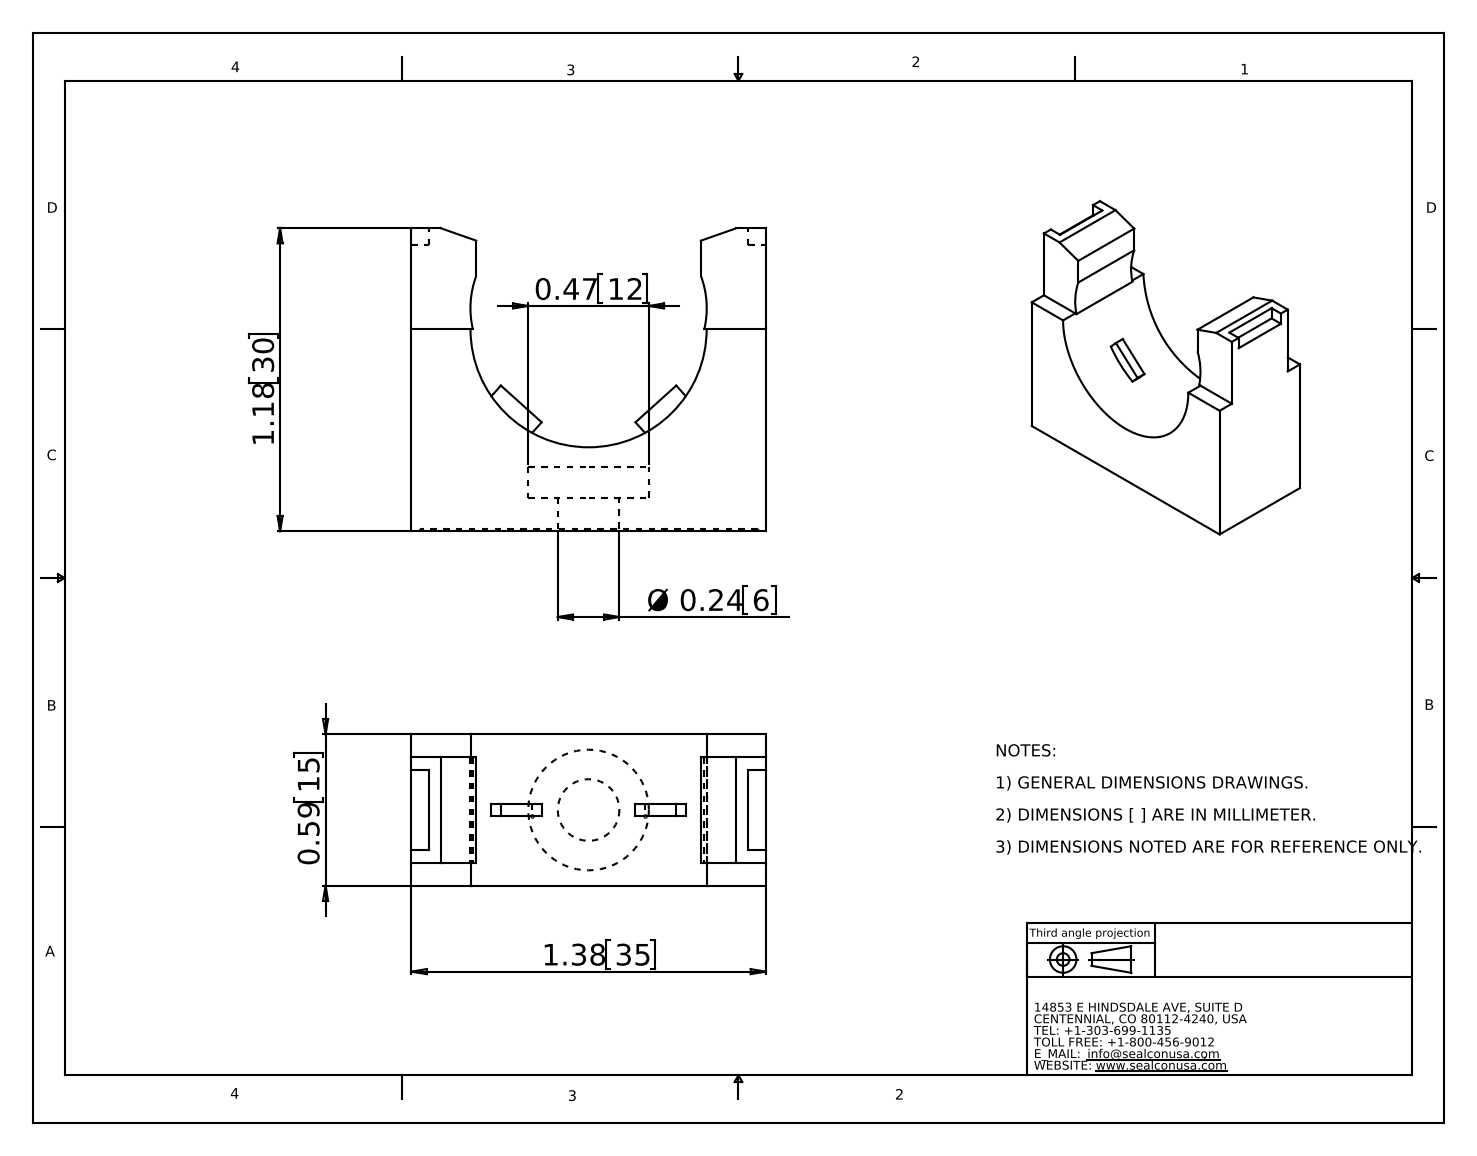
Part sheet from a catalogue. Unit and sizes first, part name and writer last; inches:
Units: inches
Overall size (bounding box): 1.38 × 1.18 × 0.59
Round holes (diameter × count): ⌀0.24 ×1, ⌀0.47 ×1
Partial cylindrical surfaces — rounded edges, fillets, slot ends (radius × count): R0.36 ×2, R0.46 ×1
Main face-to-face distances: 0.59, 1.38, 0.5, 0.09, 0.089, 0.411, 0.501, 0.24, 0.13, 0.12
Volume: 0.486 in³ · Surface area: 6.029 in²
Bodies: 1 solid, 54 faces (46 planar, 8 cylindrical, 0 other)
Part name (STEP PRODUCT): MB-16-BK
STEP written by: SolidWorks 2008 (CONFIG_CONTROL_DESIGN)
